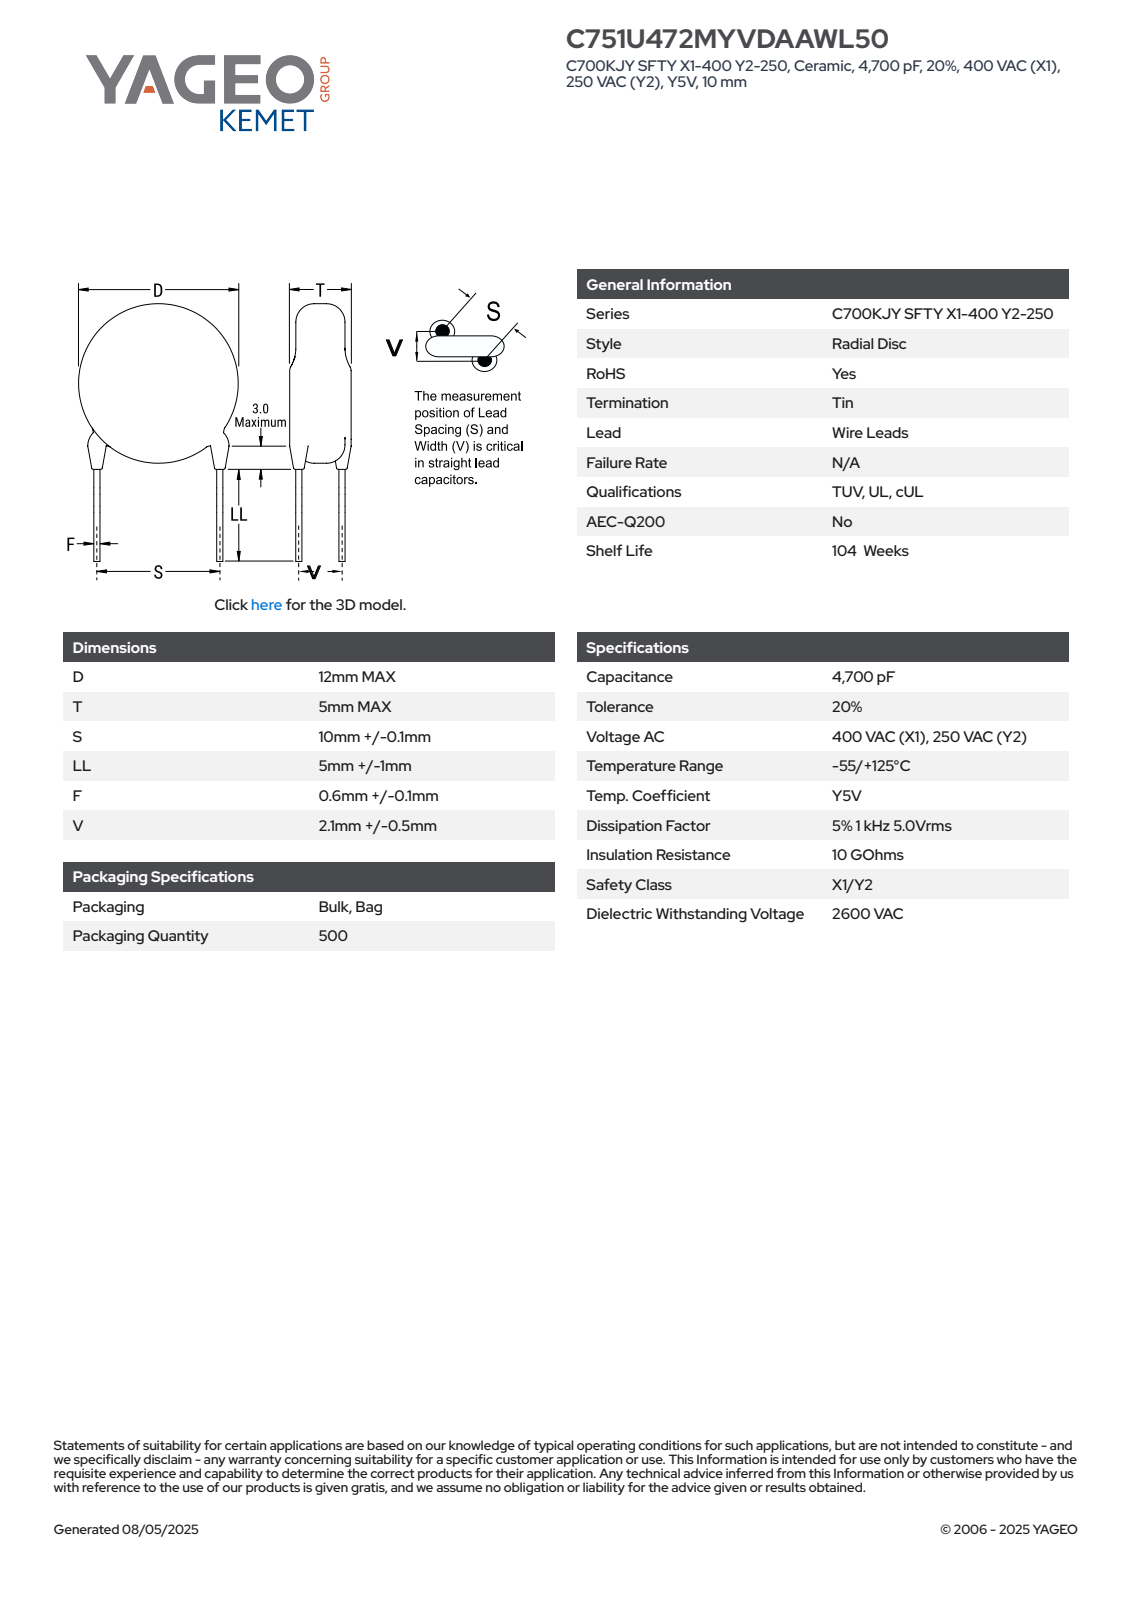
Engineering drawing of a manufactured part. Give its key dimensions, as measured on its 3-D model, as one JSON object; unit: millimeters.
{"part_name": "CCD_KST_12X5_D12T5S10.1LL6F0.7V2.1", "step_written_by": "SolidWorks 2021 (AUTOMOTIVE_DESIGN)", "units": "millimeters", "bodies": {"solids": 4, "faces": 80, "planar": 63, "cylindrical": 13, "other": 4}, "overall_size": [18.75, 12, 5], "volume_mm3": 562, "surface_area_mm2": 444, "round_bosses_or_shafts": [[1.2, 4], [0.7, 2], [12, 1]], "face_to_face_distances": [5, 6, 13.66, 7.66, 12.3, 6.3, 1.36, 0.37, 1.1, 5.55]}
